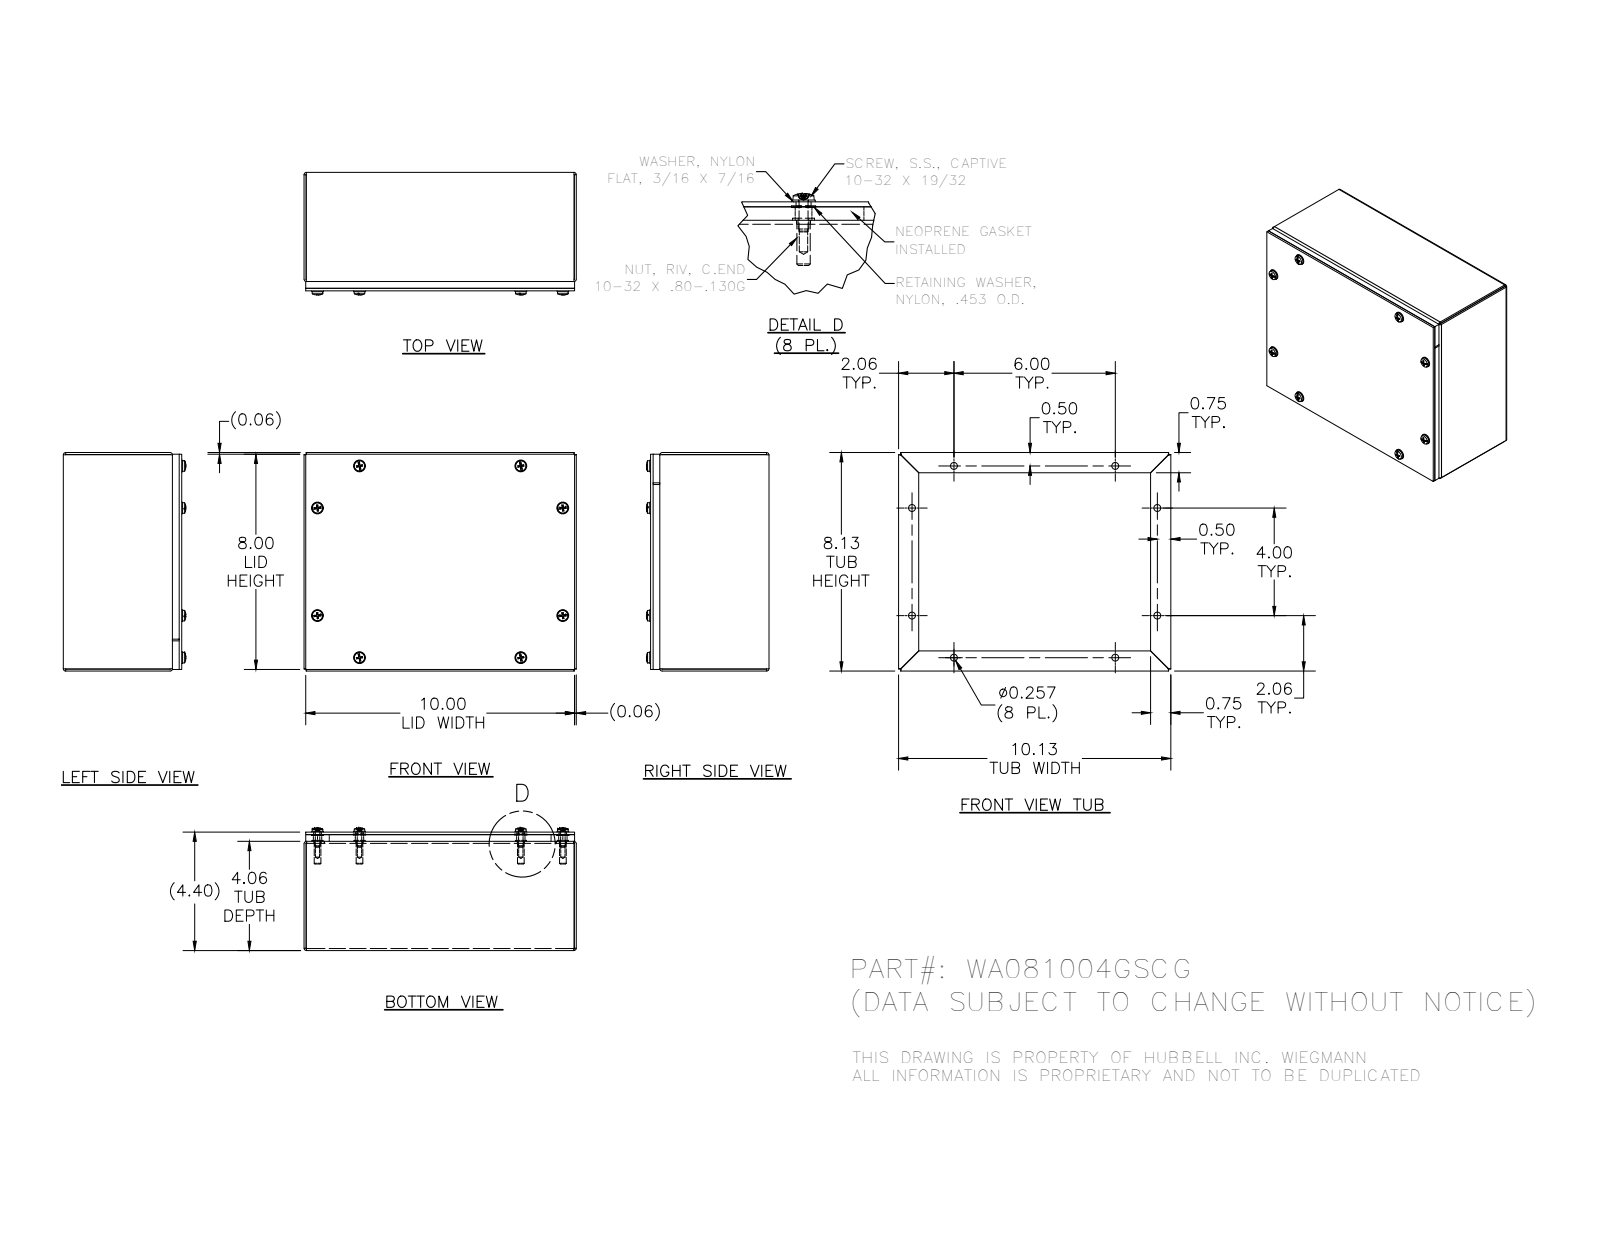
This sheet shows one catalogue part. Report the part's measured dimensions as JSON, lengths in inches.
{"part_name": "39035; 316296; 37210; WA081004GSCGBKP (+4 more)", "step_written_by": "SolidWorks 2014 (AUTOMOTIVE_DESIGN)", "units": "inches", "bodies": {"solids": 36, "faces": 892, "planar": 420, "cylindrical": 240, "other": 232}, "overall_size": [10.125, 8.125, 4.558], "volume_in3": 33.1, "surface_area_in2": 756.2, "round_holes": [[0.156, 8], [0.188, 8], [0.196, 8], [0.257, 8], [0.278, 8], [0.281, 8], [0.313, 8]], "round_bosses_or_shafts": [[0.453, 8], [0.437, 8], [0.406, 8], [0.248, 8], [0.167, 8]], "partial_cylinders_radius": [[0.016, 8], [0.089, 8], [0.09, 8]], "face_to_face_distances": [0.074, 0.094, 4.33, 4.404, 4.236, 4.31, 8.051, 3.986, 10.051, 0.344], "hole_center_spacings": [2.209, 4, 6, 5.778, 9.387, 5.778, 5.777, 7.722]}
